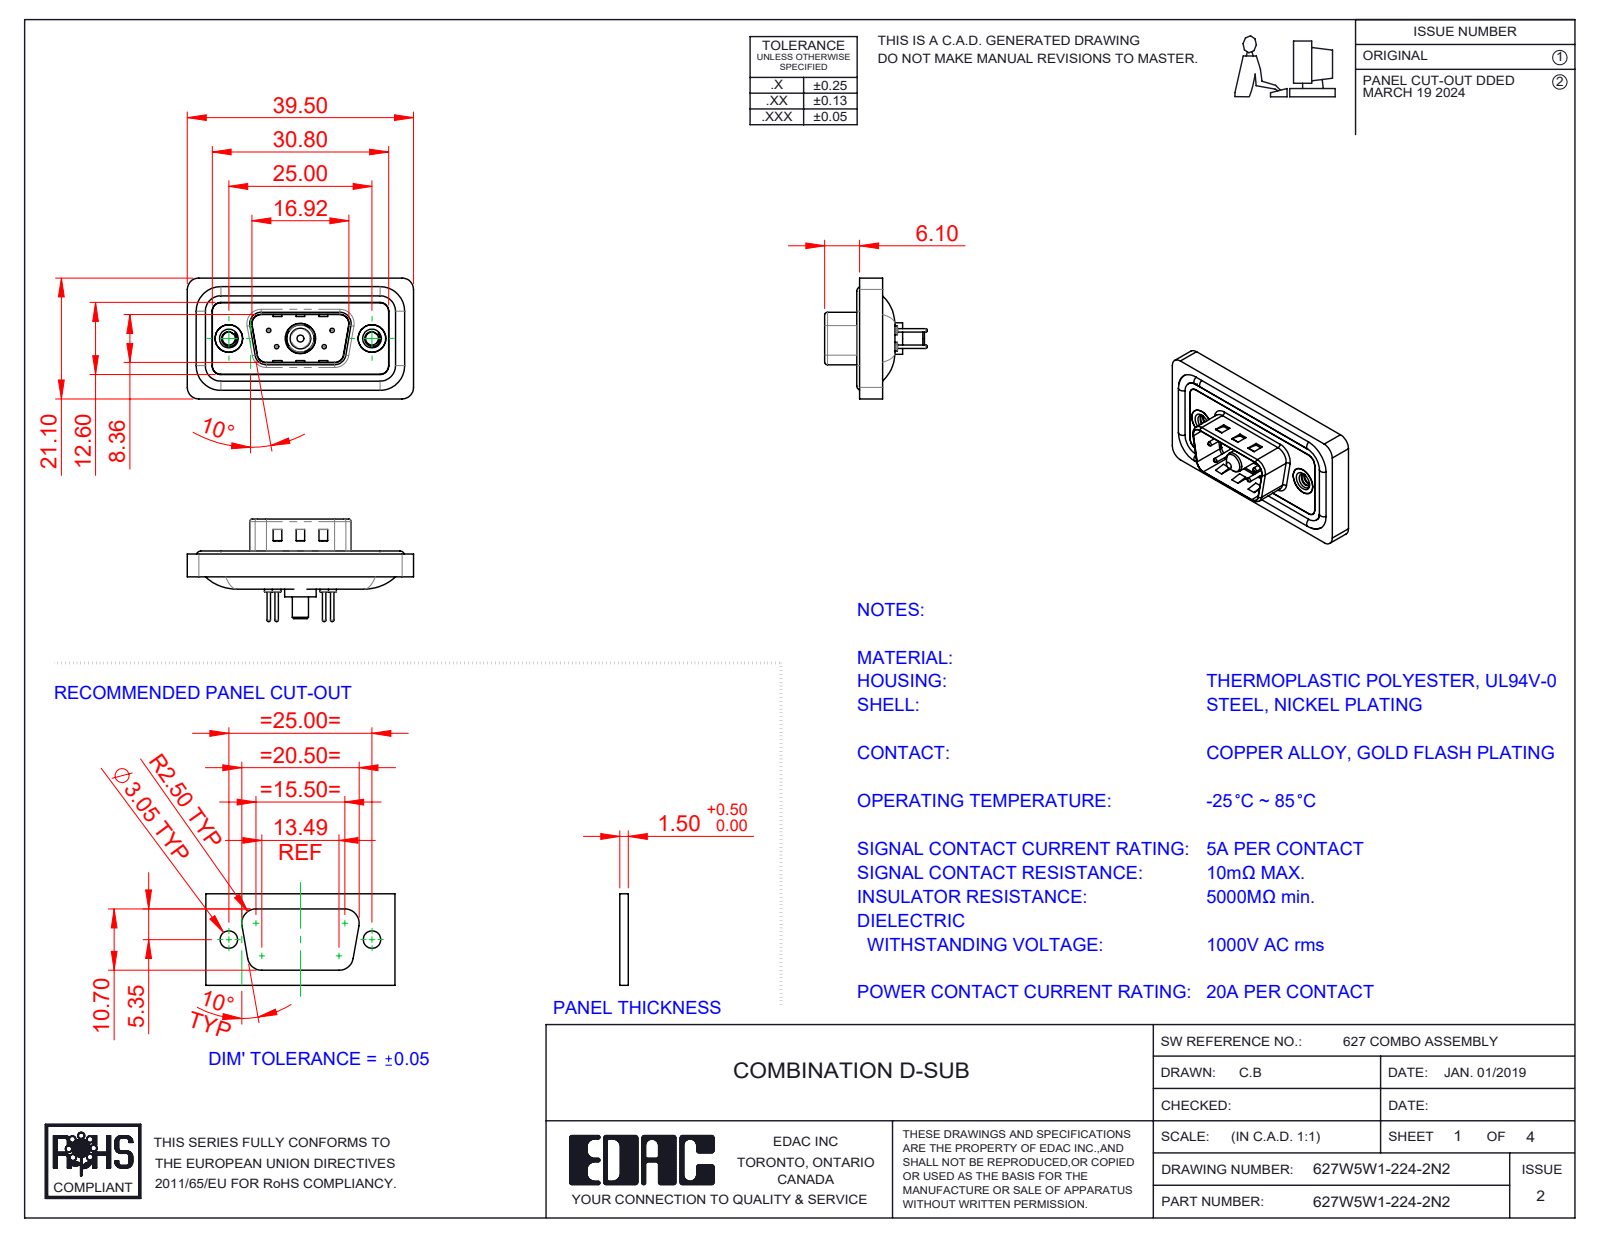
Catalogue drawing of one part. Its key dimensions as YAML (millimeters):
part_name: "627Combo Contact Row 2_24; 627Combo Shell Front_09 Contacts; 627Combo Waterproof Housing_09 Contacts; 627Combo Threaded Rivet_2 (+5 more)"
step_written_by: "SolidWorks 2023 (CONFIG_CONTROL_DESIGN)"
units: millimeters
bodies: {solids: 13, faces: 598, planar: 183, cylindrical: 255, other: 160}
overall_size: [39.5, 21.1, 17.9]
volume: 4388
surface_area: 6941
round_holes:
  - {diameter: 0.75, count: 4}
  - {diameter: 1.6, count: 4}
  - {diameter: 2, count: 4}
  - {diameter: 2.26, count: 2}
  - {diameter: 4, count: 2}
  - {diameter: 4.8, count: 2}
  - {diameter: 5, count: 2}
  - {diameter: 4.85, count: 1}
  - {diameter: 5.3, count: 1}
round_bosses_or_shafts:
  - {diameter: 1.6, count: 4}
  - {diameter: 1.5, count: 4}
  - {diameter: 0.6, count: 4}
  - {diameter: 4.9, count: 2}
  - {diameter: 5.5, count: 1}
  - {diameter: 5.2, count: 1}
  - {diameter: 4.75, count: 1}
  - {diameter: 3.75, count: 1}
partial_cylinders:
  - {radius: 1.5, count: 22}
  - {radius: 2, count: 18}
  - {radius: 0.5, count: 8}
  - {radius: 1.6, count: 8}
  - {radius: 0.25, count: 4}
  - {radius: 0.6, count: 4}
  - {radius: 0.65, count: 4}
  - {radius: 0.9, count: 4}
face_to_face_distances: [0.4, 1.1, 2.9, 1.6, 1.5, 3.1, 0.5, 2.5, 4, 0.8]
hole_center_spacings: [3.16, 5.72, 7.1, 12.5, 18.1, 4.39, 4.4, 8.31]
